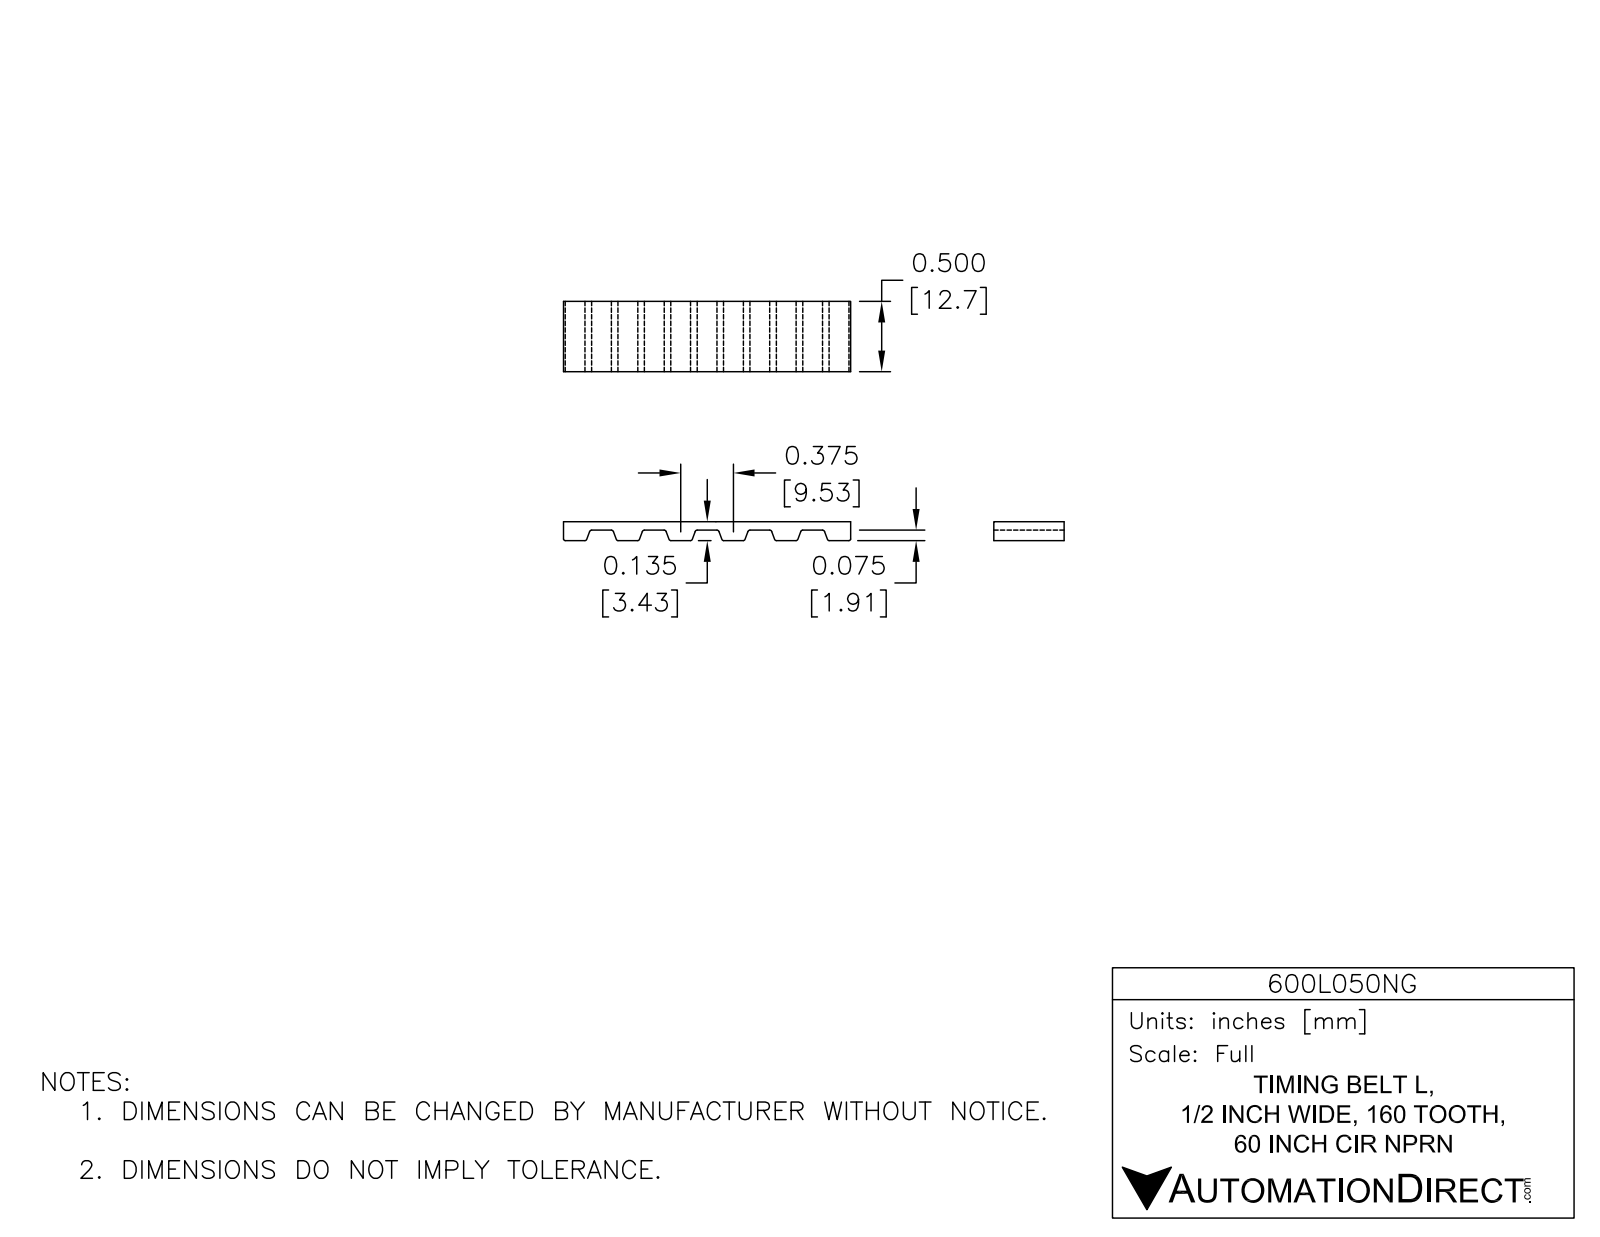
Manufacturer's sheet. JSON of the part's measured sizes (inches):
{"part_name": "600L050NG", "step_written_by": "SolidWorks 2014 (AUTOMOTIVE_DESIGN)", "units": "inches", "bodies": {"solids": 1, "faces": 1298, "planar": 618, "cylindrical": 680, "other": 0}, "overall_size": [28.288, 3, 0.5], "volume_in3": 2.727, "surface_area_in2": 77.91, "partial_cylinders_radius": [[0.02, 638], [1.435, 2], [1.5, 2]], "face_to_face_distances": [0.065, 2.935, 3, 2.87, 0.5, 0.14, 2.86, 0.075, 2.795, 2.72]}
